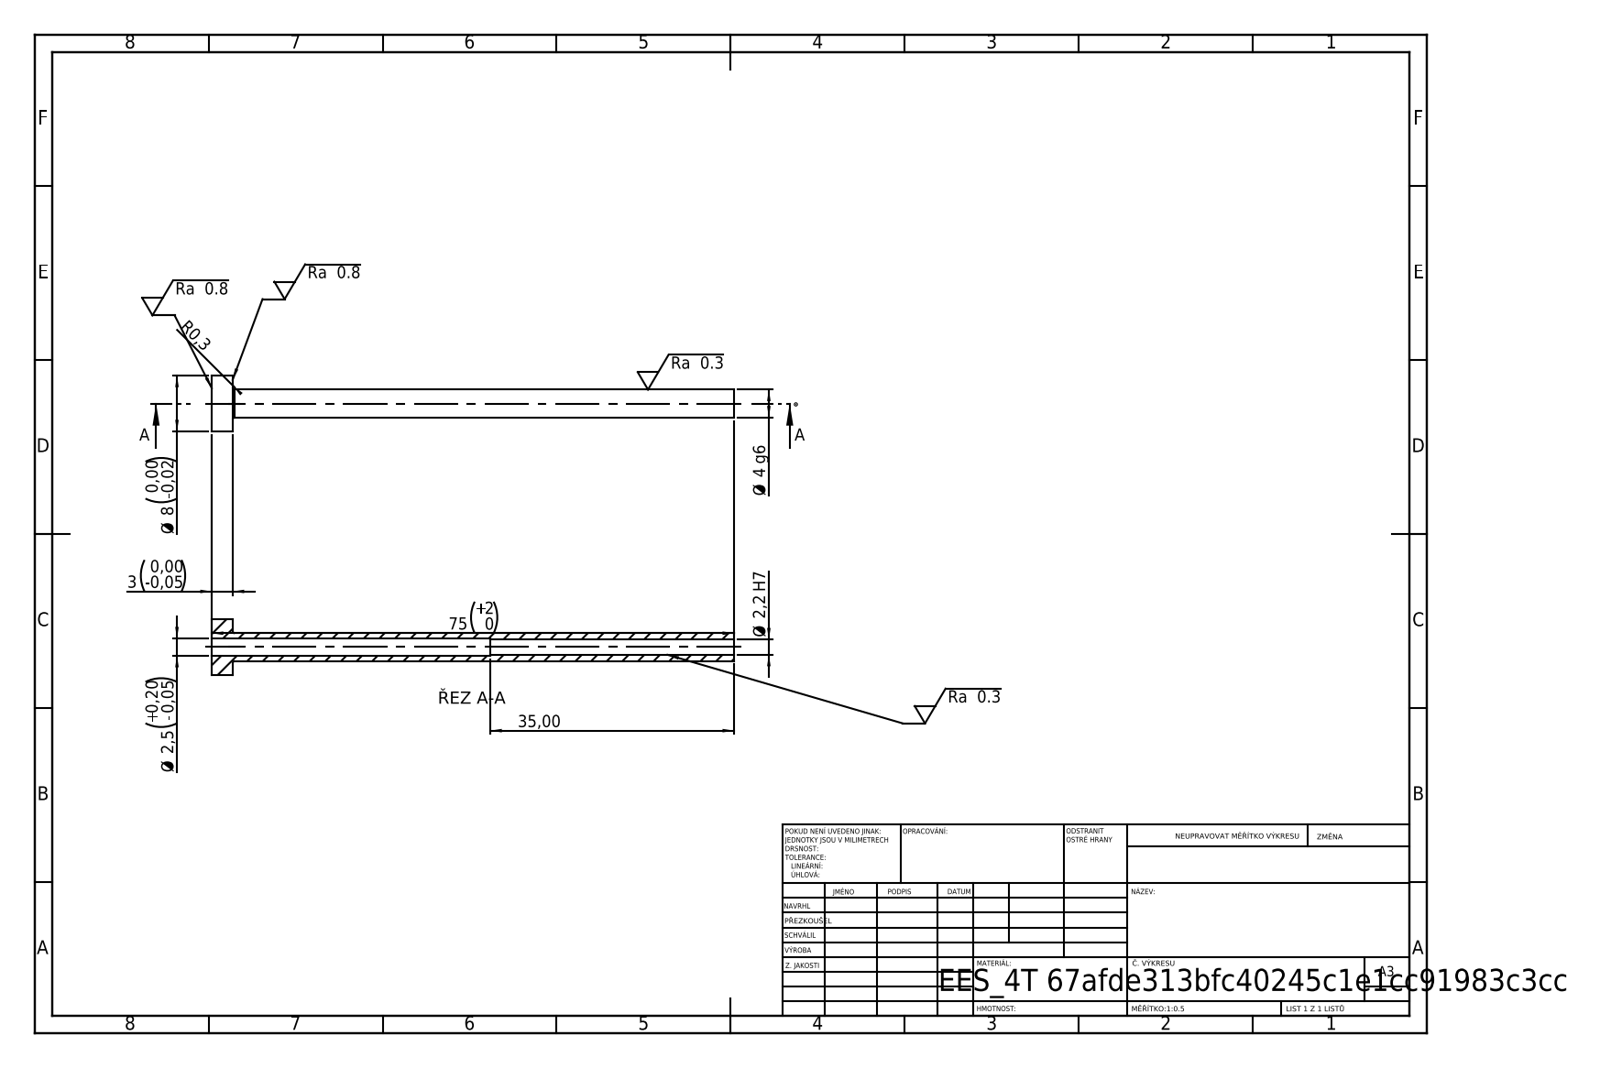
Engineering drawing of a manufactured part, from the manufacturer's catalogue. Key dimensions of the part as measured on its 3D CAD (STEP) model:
STEP written by: SolidWorks 2019 (CONFIG_CONTROL_DESIGN)
Units: millimetres
Bodies: 1 solid, 14 faces (4 planar, 8 cylindrical, 2 other)
Overall size (bounding box): 75 × 8 × 8
Volume: 726 mm³ · Surface area: 1 628 mm²
Round holes (diameter × count): ⌀2.2 ×1, ⌀2.5 ×1
Round bosses / shafts (diameter × count): ⌀8 ×1, ⌀4 ×1
Main face-to-face distances: 3, 75, 72, 40, 37, 35
